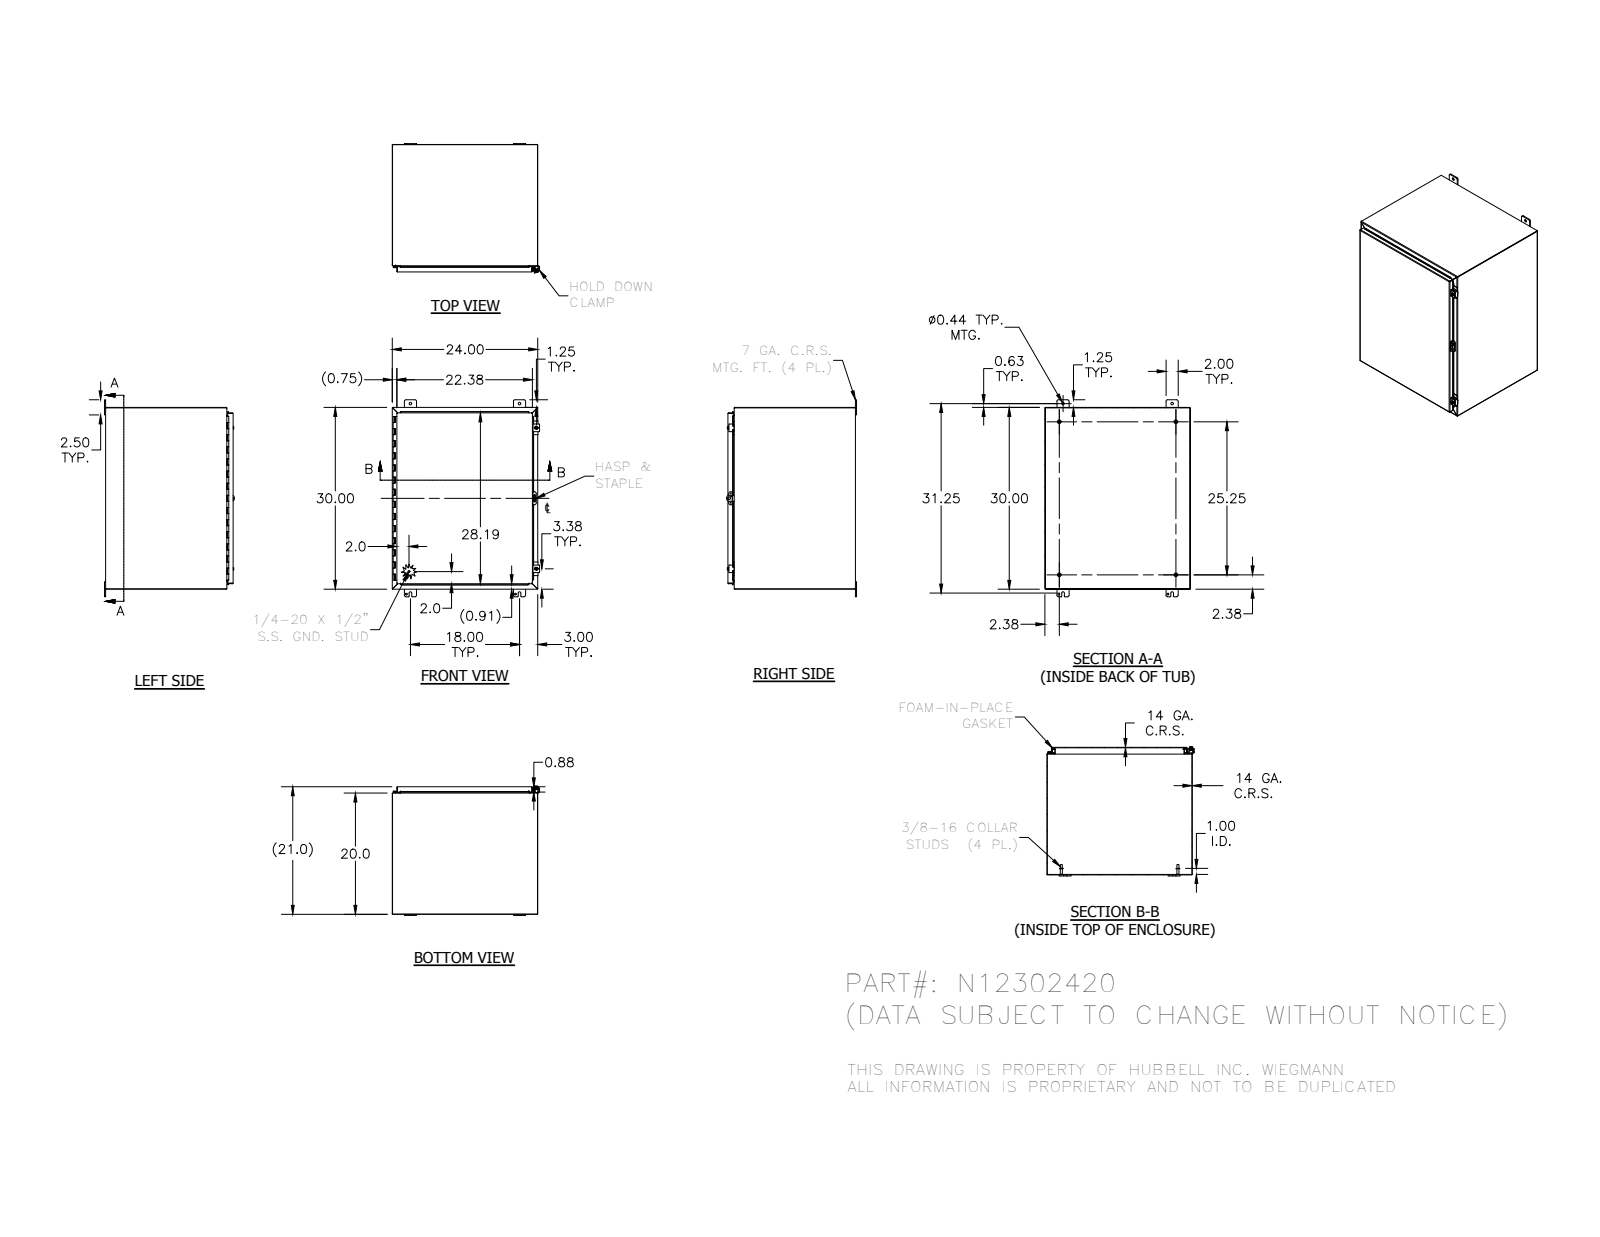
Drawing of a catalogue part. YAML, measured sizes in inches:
part_name: "N12302420; 34840; 38413; N122420TB (+8 more)"
step_written_by: "Autodesk Inventor 2012 (AUTOMOTIVE_DESIGN)"
units: inches
bodies: {solids: 29, faces: 918, planar: 540, cylindrical: 277, other: 101}
overall_size: [32.5, 24.311, 21.41]
volume: 301.4
surface_area: 7993
round_holes:
  - {diameter: 0.313, count: 4}
  - {diameter: 0.438, count: 4}
  - {diameter: 0.11, count: 3}
  - {diameter: 0.211, count: 2}
  - {diameter: 0.281, count: 2}
  - {diameter: 0.3, count: 2}
  - {diameter: 0.125, count: 1}
  - {diameter: 0.156, count: 1}
  - {diameter: 0.5, count: 1}
round_bosses_or_shafts:
  - {diameter: 0.625, count: 4}
  - {diameter: 0.33, count: 4}
  - {diameter: 0.25, count: 4}
  - {diameter: 0.52, count: 2}
  - {diameter: 0.5, count: 2}
  - {diameter: 0.35, count: 2}
  - {diameter: 0.115, count: 2}
  - {diameter: 0.337, count: 1}
partial_cylinders:
  - {radius: 0.03, count: 27}
  - {radius: 0.125, count: 25}
  - {radius: 0.25, count: 25}
  - {radius: 0.031, count: 21}
  - {radius: 0.105, count: 21}
  - {radius: 0.063, count: 13}
  - {radius: 0.1, count: 4}
  - {radius: 0.141, count: 4}
face_to_face_distances: [0.074, 20.959, 23.926, 29.926, 20.885, 21.033, 23.852, 24, 29.852, 30]
hole_center_spacings: [1.593, 18, 30, 34.986, 0.791, 17.372, 18.742, 28.571]
